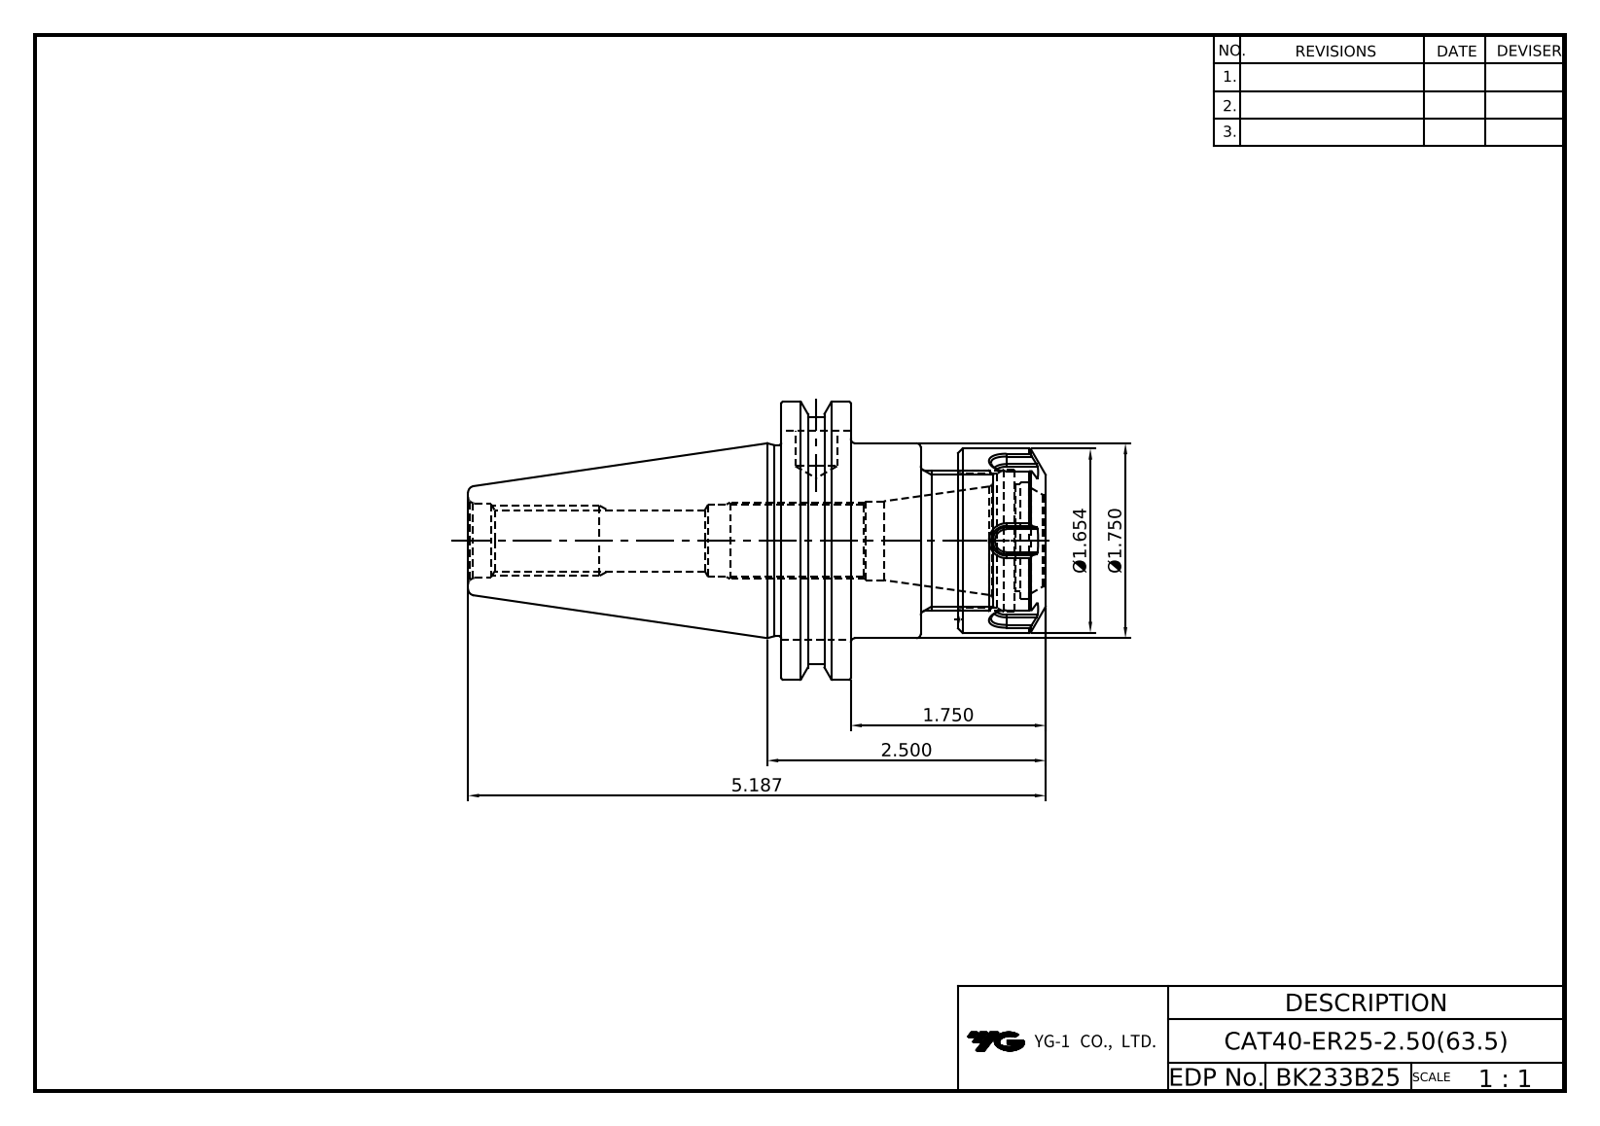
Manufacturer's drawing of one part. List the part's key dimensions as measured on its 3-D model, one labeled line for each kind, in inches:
Part name (STEP PRODUCT): LO-CAT40-ER25-63.5; ER25NUT
STEP written by: Autodesk Inventor 2025 (AUTOMOTIVE_DESIGN)
Units: inches
Bodies: 2 solids, 141 faces (65 planar, 32 cylindrical, 44 other)
Overall size (bounding box): 5.187 × 2.5 × 2.405
Volume: 8.481 in³ · Surface area: 50.71 in²
Round holes (diameter × count): ⌀0.375 ×1, ⌀0.527 ×1, ⌀0.62 ×1, ⌀0.642 ×1, ⌀0.709 ×1, ⌀0.823 ×1, ⌀0.906 ×1, ⌀1.055 ×1, ⌀1.201 ×1, ⌀1.28 ×1
Round bosses / shafts (diameter × count): ⌀2.5 ×1, ⌀2.217 ×1, ⌀1.75 ×1, ⌀1.717 ×1, ⌀1.654 ×1, ⌀1.26 ×1
Partial cylindrical surfaces — rounded edges, fillets, slot ends (radius × count): R0.02 ×12
Main face-to-face distances: 0.625, 1.253, 0.628, 1.588, 0.963, 0.335, 2.096, 1.47, 0.843, 0.508
